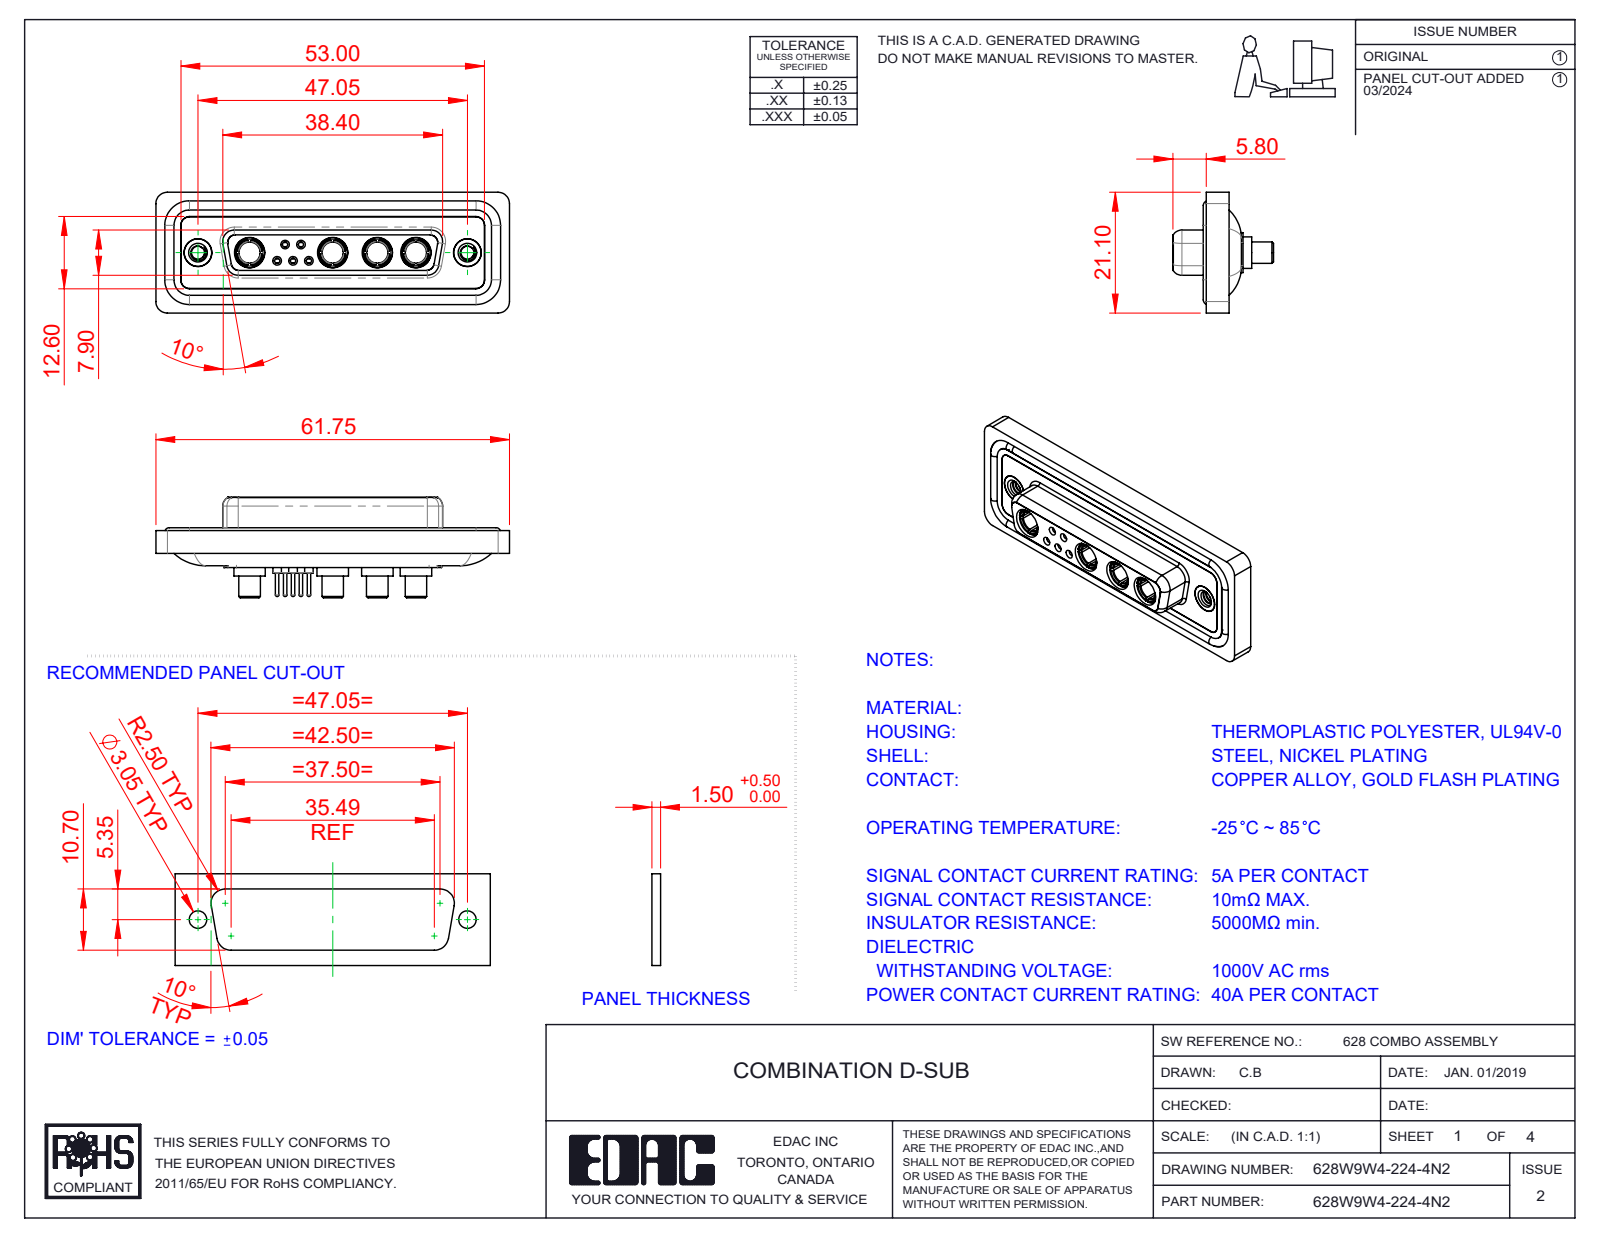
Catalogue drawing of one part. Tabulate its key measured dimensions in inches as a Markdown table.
| quantity | value |
| --- | --- |
| part name | 628Combo Contact Row 2_24; 628Combo Shell Front_25 Contacts; 628Combo Contact Row 1_24; 628W9W4-224-4N2 (+5 more) |
| STEP written by | SolidWorks 2023 (CONFIG_CONTROL_DESIGN) |
| units | inches |
| bodies | 20 solids, 957 faces (296 planar, 375 cylindrical, 286 other) |
| overall size | 2.431 × 0.831 × 0.691 |
| volume | 0.506 in³ |
| surface area | 21.09 in² |
| round holes (diameter × count) | 0.191 × 6, 0.035 × 5, 0.043 × 5, 0.059 × 5, 0.079 × 5, 0.146 × 4, 0.209 × 4, 0.063 × 3, 0.067 × 2, 0.089 × 2, 0.157 × 2, 0.159 × 2 |
| round bosses / shafts (diameter × count) | 0.063 × 6, 0.087 × 5, 0.024 × 5, 0.217 × 4, 0.205 × 4, 0.195 × 4, 0.187 × 4, 0.148 × 4 |
| partial cylindrical surfaces (radius × count) | 0.059 × 22, 0.079 × 18, 0.053 × 8, 0.063 × 8, 0.01 × 4, 0.02 × 4, 0.024 × 4, 0.026 × 4 |
| main face-to-face distances | 0.016, 0.071, 0.293, 0.222, 0.02, 0.278, 0.26, 0.063, 0.043, 0.114 |
| hole center spacings | 0.124, 0.109, 0.198, 0.109, 0.173, 0.198, 0.218, 0.226 |
